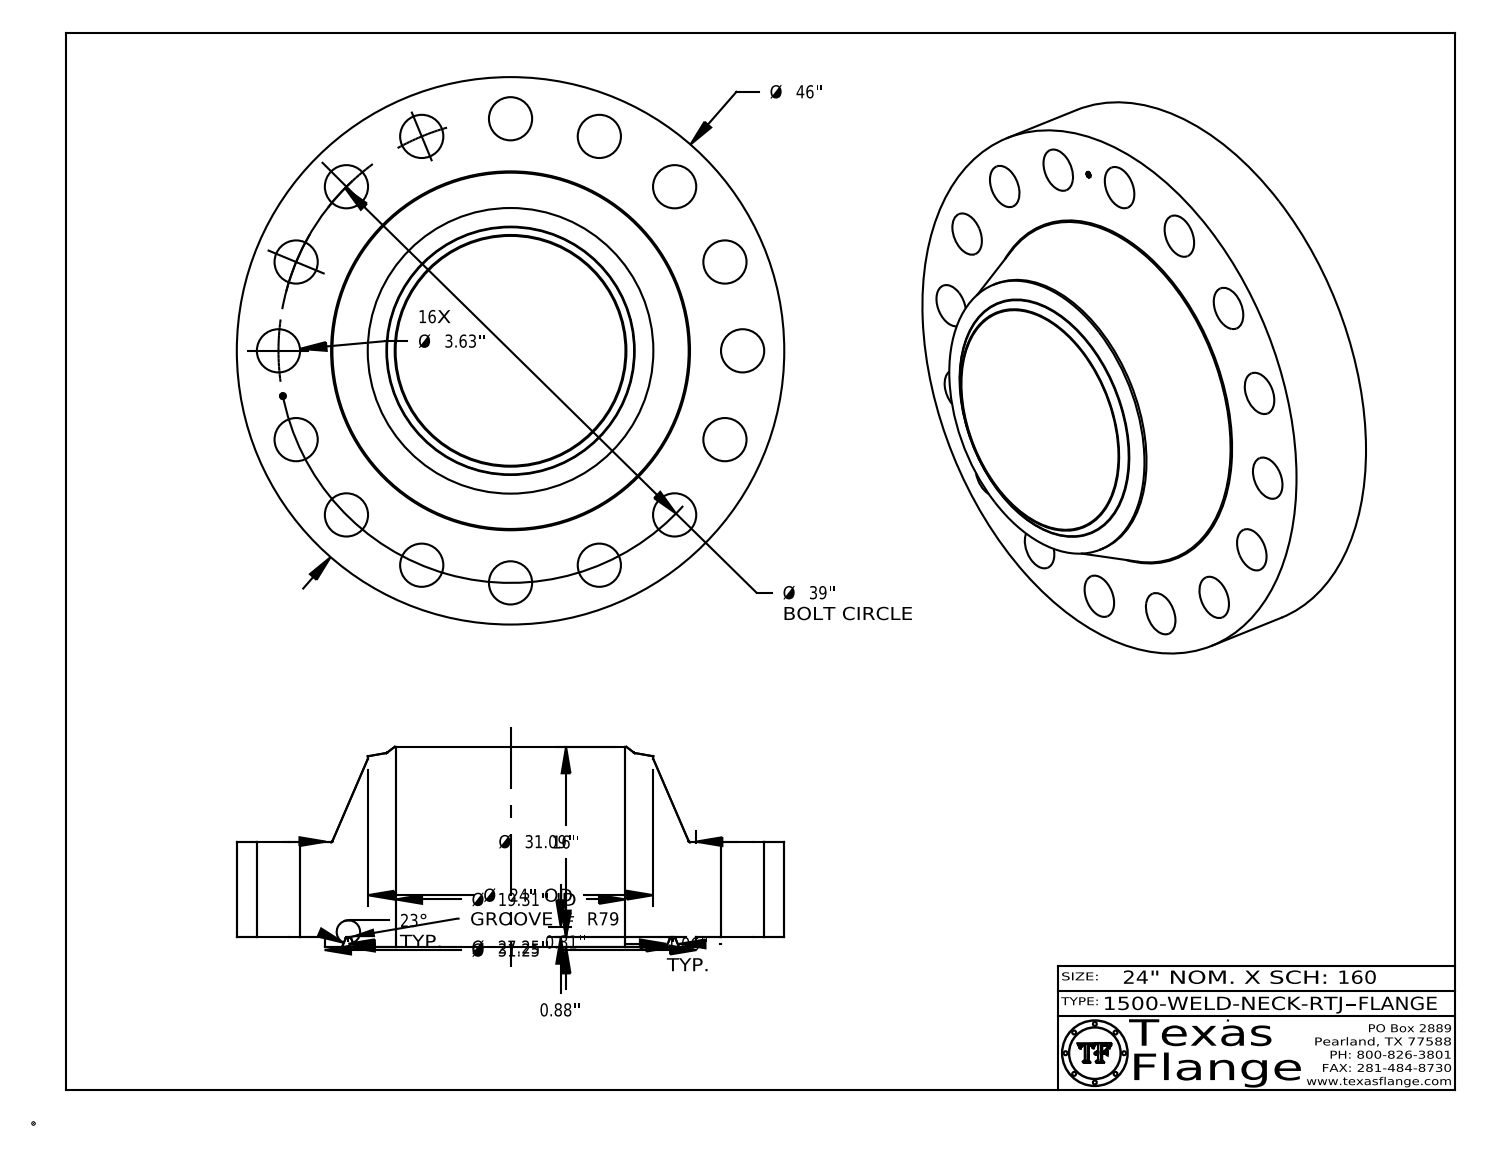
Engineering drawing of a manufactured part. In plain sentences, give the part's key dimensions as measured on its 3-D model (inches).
The part is named "1500-WELD-NECK-RTJ". Its 3-D file was written by "CATIA V5 STEP AP214 (AUTOMOTIVE_DESIGN)". It is 1 solid with 449 faces: 371 planar, 60 cylindrical and 18 other. Overall it measures 46 by 46 by 16.813 inches. Its volume is 12 008 cubic inches and its surface area 6 630 square inches. Round holes: 16 of diameter 3.63, 1 of diameter 0.495, 1 of diameter 19.312. Round bosses or shafts: 8 of diameter 0.03, 1 of diameter 46, 1 of diameter 31.25, 1 of diameter 24, 1 of diameter 0.39. The main face-to-face distances are 8, 0.813, 8.813, 16.813, 16, 8.798, 7.985, 0.015, 8.015, 0.148. The hole center spacings are 19.5, 21.667, 27.577, 38.251, 14.925, 36.031, 7.608, 7.609.
